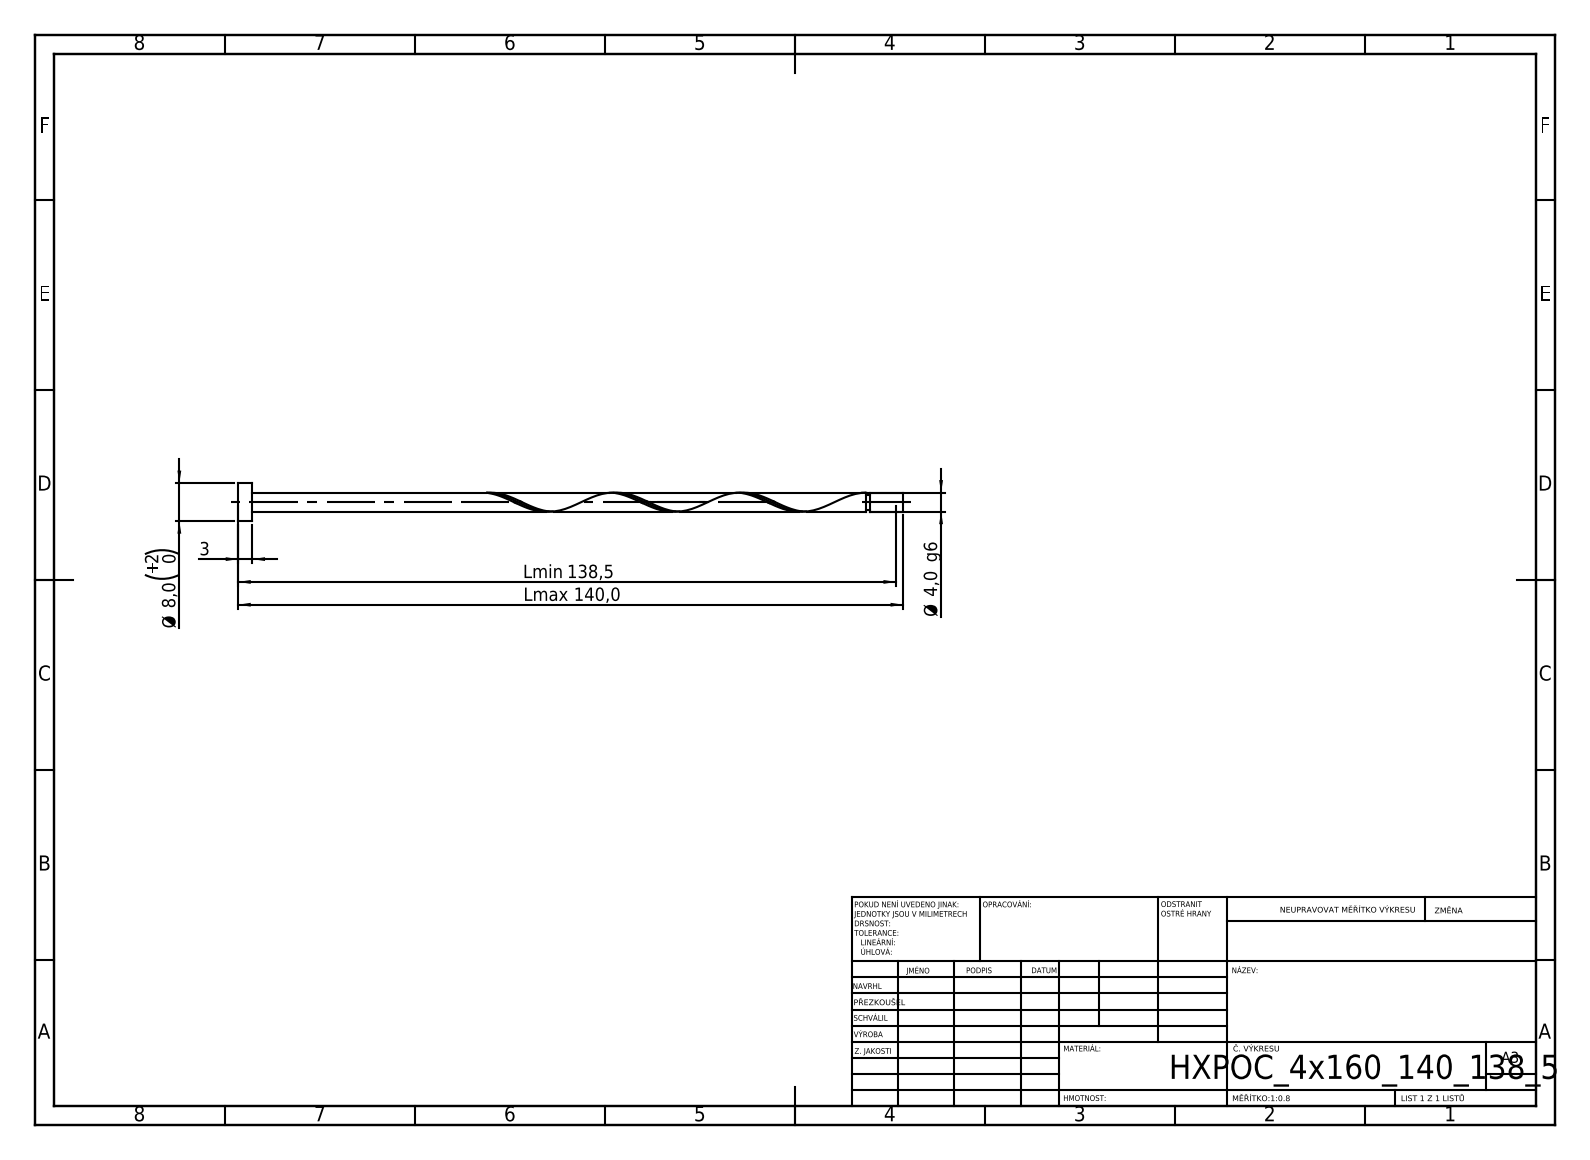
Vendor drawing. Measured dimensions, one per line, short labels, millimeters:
written by: SolidWorks 2019 (CONFIG_CONTROL_DESIGN)
unit: mm
bodies: 1 solid, 21 faces (6 planar, 14 cylindrical, 1 other)
size: 140 × 8 × 8
volume: 1 850 mm³; area: 1 939 mm²
bosses: 1× ⌀8, 1× ⌀4, 1× ⌀3.2
face distances: 3, 140, 137, 133.02, 130.02, 6.98, 132.22, 129.22, 0.8, 7.78
